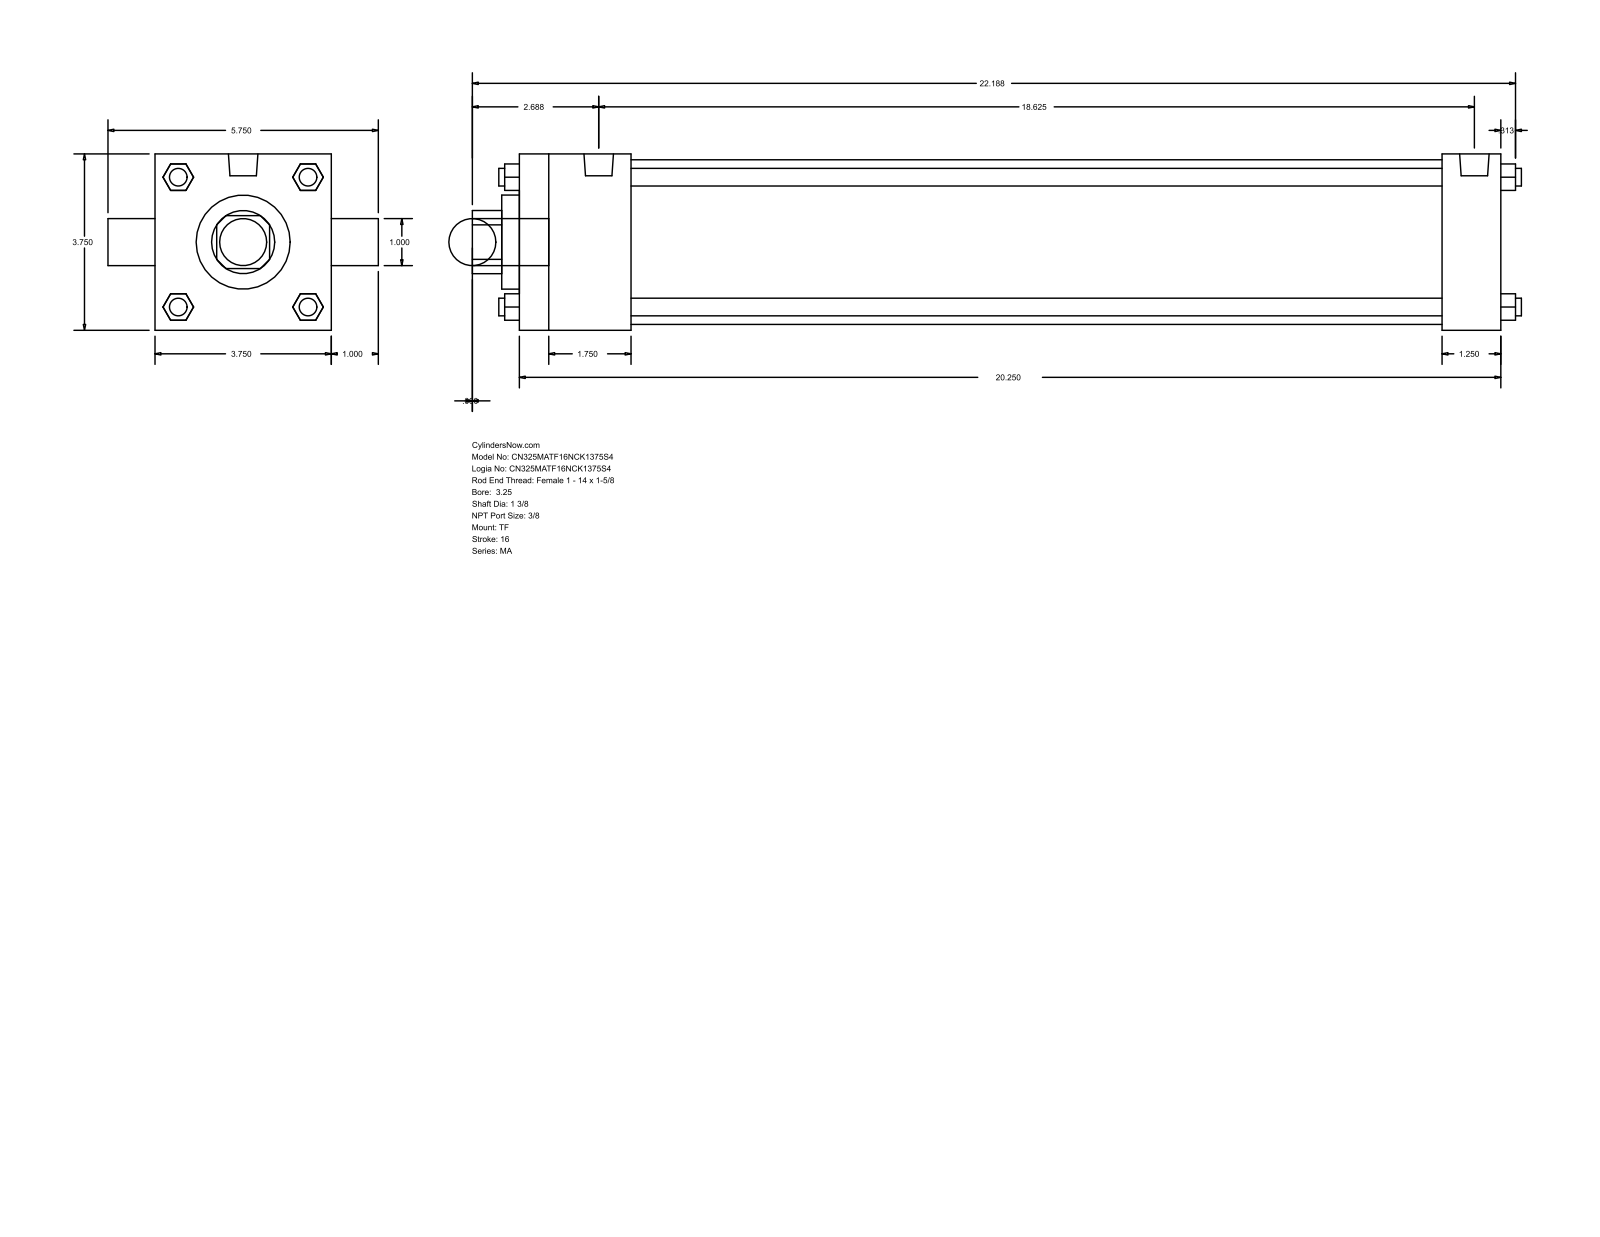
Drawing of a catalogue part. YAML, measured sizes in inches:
part_name: "MA_TF__0325_1.375"
step_written_by: "GSSL Pune (CONFIG_CONTROL_DESIGN)"
units: inches
bodies: {solids: 0, faces: 120, planar: 92, cylindrical: 28, other: 0}
overall_size: [22.313, 5.75, 3.75]
round_holes:
  - {diameter: 1, count: 1}
  - {diameter: 1.375, count: 1}
  - {diameter: 2, count: 1}
  - {diameter: 3.5, count: 1}
round_bosses_or_shafts:
  - {diameter: 0.375, count: 4}
  - {diameter: 0.437, count: 3}
  - {diameter: 0.627, count: 2}
  - {diameter: 1, count: 1}
partial_cylinders:
  - {radius: 0.672, count: 1}
face_to_face_distances: [3.75, 20.875, 2.375, 19.625, 17.25, 18.5, 1.25, 0.375, 2.75, 20]
